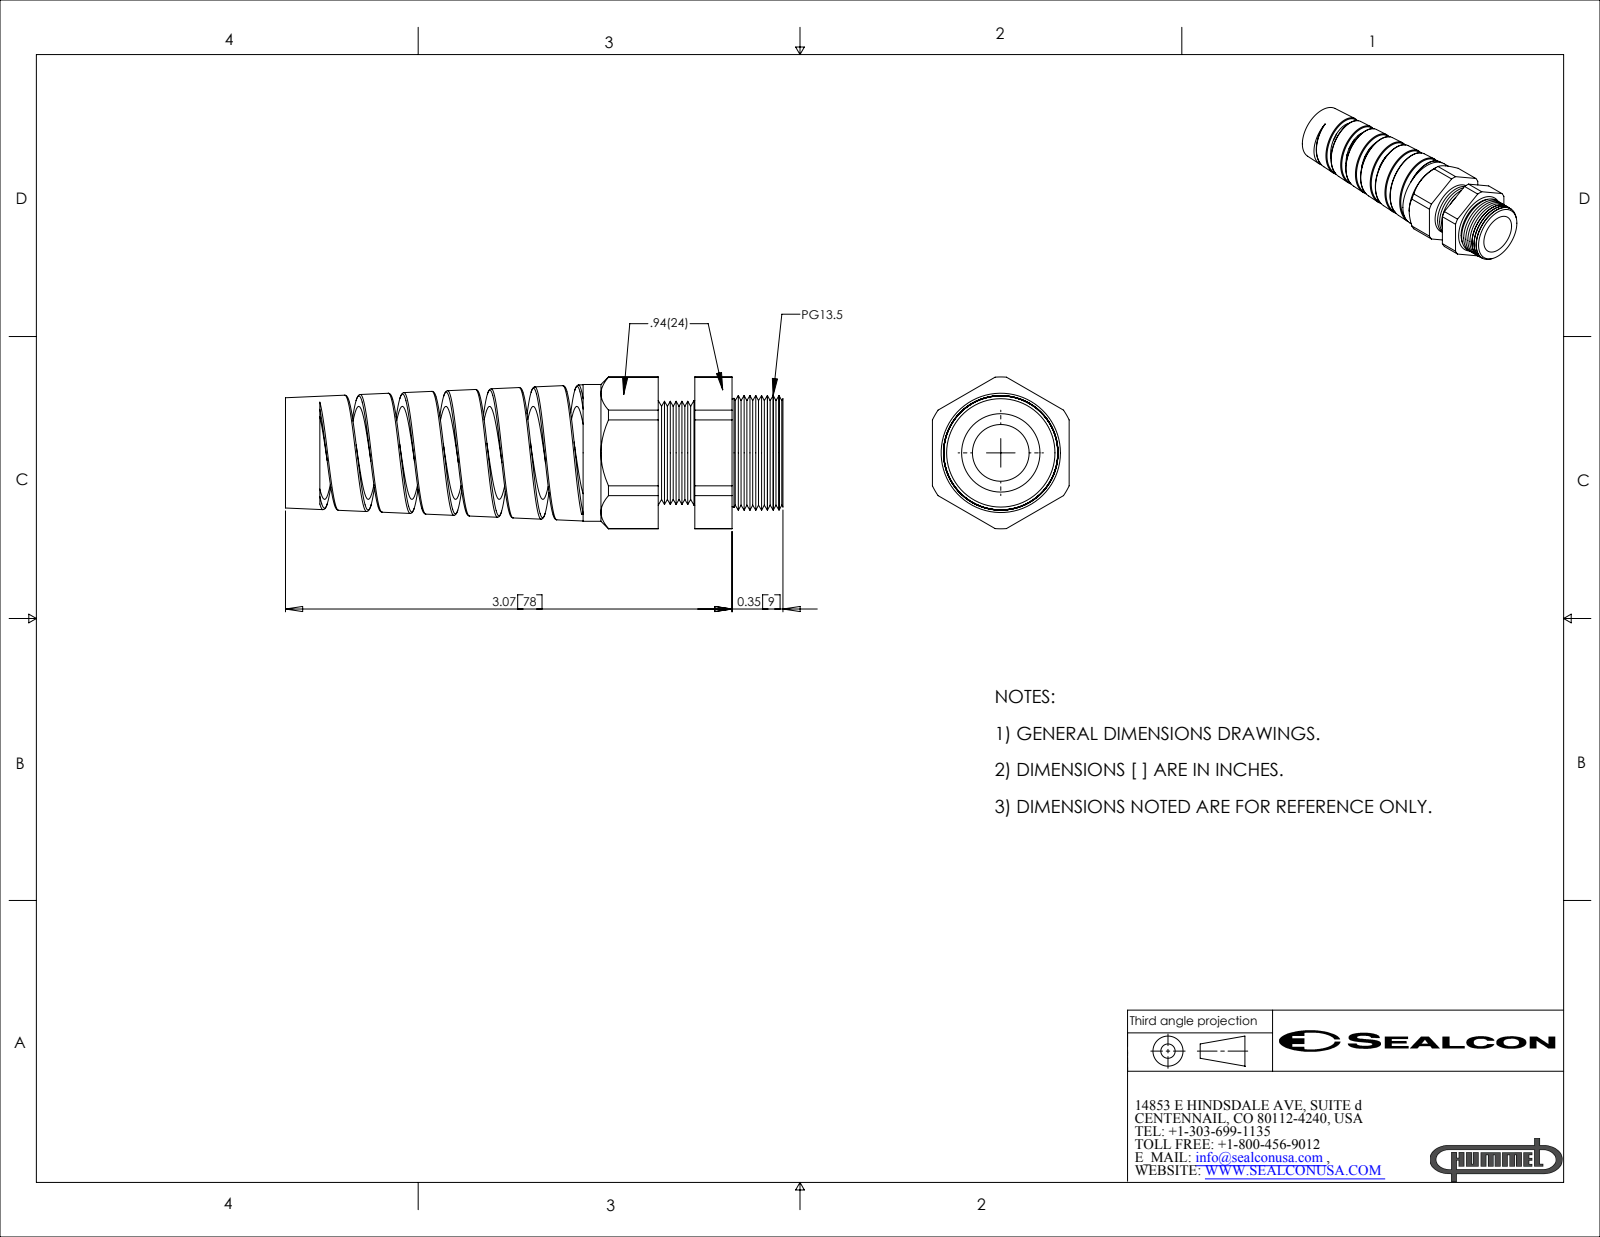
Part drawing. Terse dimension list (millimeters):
name: CF13BA-BK
written by: SolidWorks 2007 (CONFIG_CONTROL_DESIGN)
unit: mm
bodies: 2 solids, 161 faces (24 planar, 37 cylindrical, 100 other)
size: 86.9 × 26.5 × 23.9
volume: 16 000 mm³; area: 13 600 mm²
holes: 1× ⌀9.9, 1× ⌀16.3
bosses: 1× ⌀23.9, 1× ⌀18.3
rounds: 1× R8.4, 1× R13.3
face distances: 23.9, 6.4, 12.9, 6.5, 21.8, 15.4, 8.9, 11.2, 17.6, 24.1
